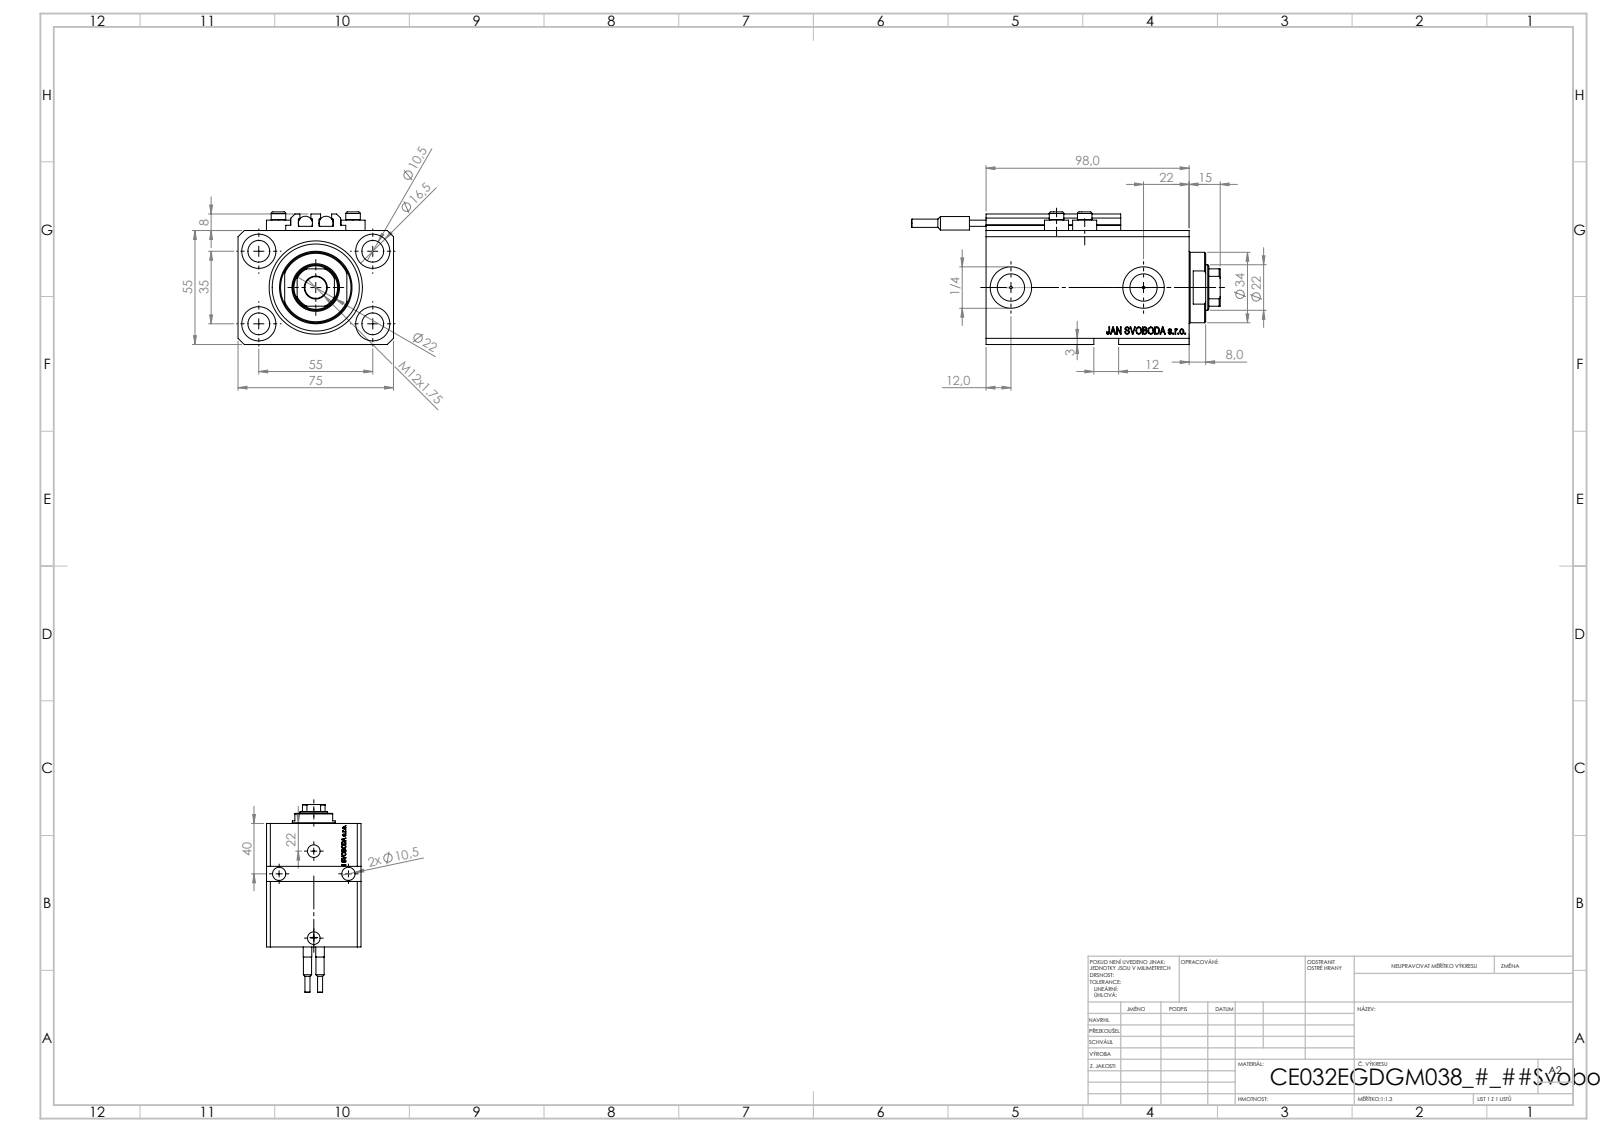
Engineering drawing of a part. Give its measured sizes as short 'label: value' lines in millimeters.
name: SWITCH_V250CE; ALLEN BOLT V250CE; V250CE_VC_E; V250CE_C_VCP (+1 more)
written by: SolidWorks 2019 (CONFIG_CONTROL_DESIGN)
unit: mm
bodies: 10 solids, 1132 faces (550 planar, 150 cylindrical, 432 other)
size: 149 × 75 × 64
volume: 346 176 mm³; area: 90 158 mm²
holes: 7× ⌀10.5, 4× ⌀1.25, 4× ⌀4, 4× ⌀16.5, 2× ⌀10, 2× ⌀13.16, 2× ⌀20, 1× ⌀22, 1× ⌀32, 1× ⌀45
bosses: 4× ⌀11.6, 4× ⌀7, 2× ⌀6.8, 2× ⌀6.5, 2× ⌀4, 1× ⌀34
rounds: 10× R0.2, 1× R10.5
face distances: 55, 75, 3, 15, 98, 83, 9.9, 57, 73.1, 88.1
hole spacings: 32.6, 55, 13.6, 14.09, 25.81, 32.01, 32.45, 32.87
